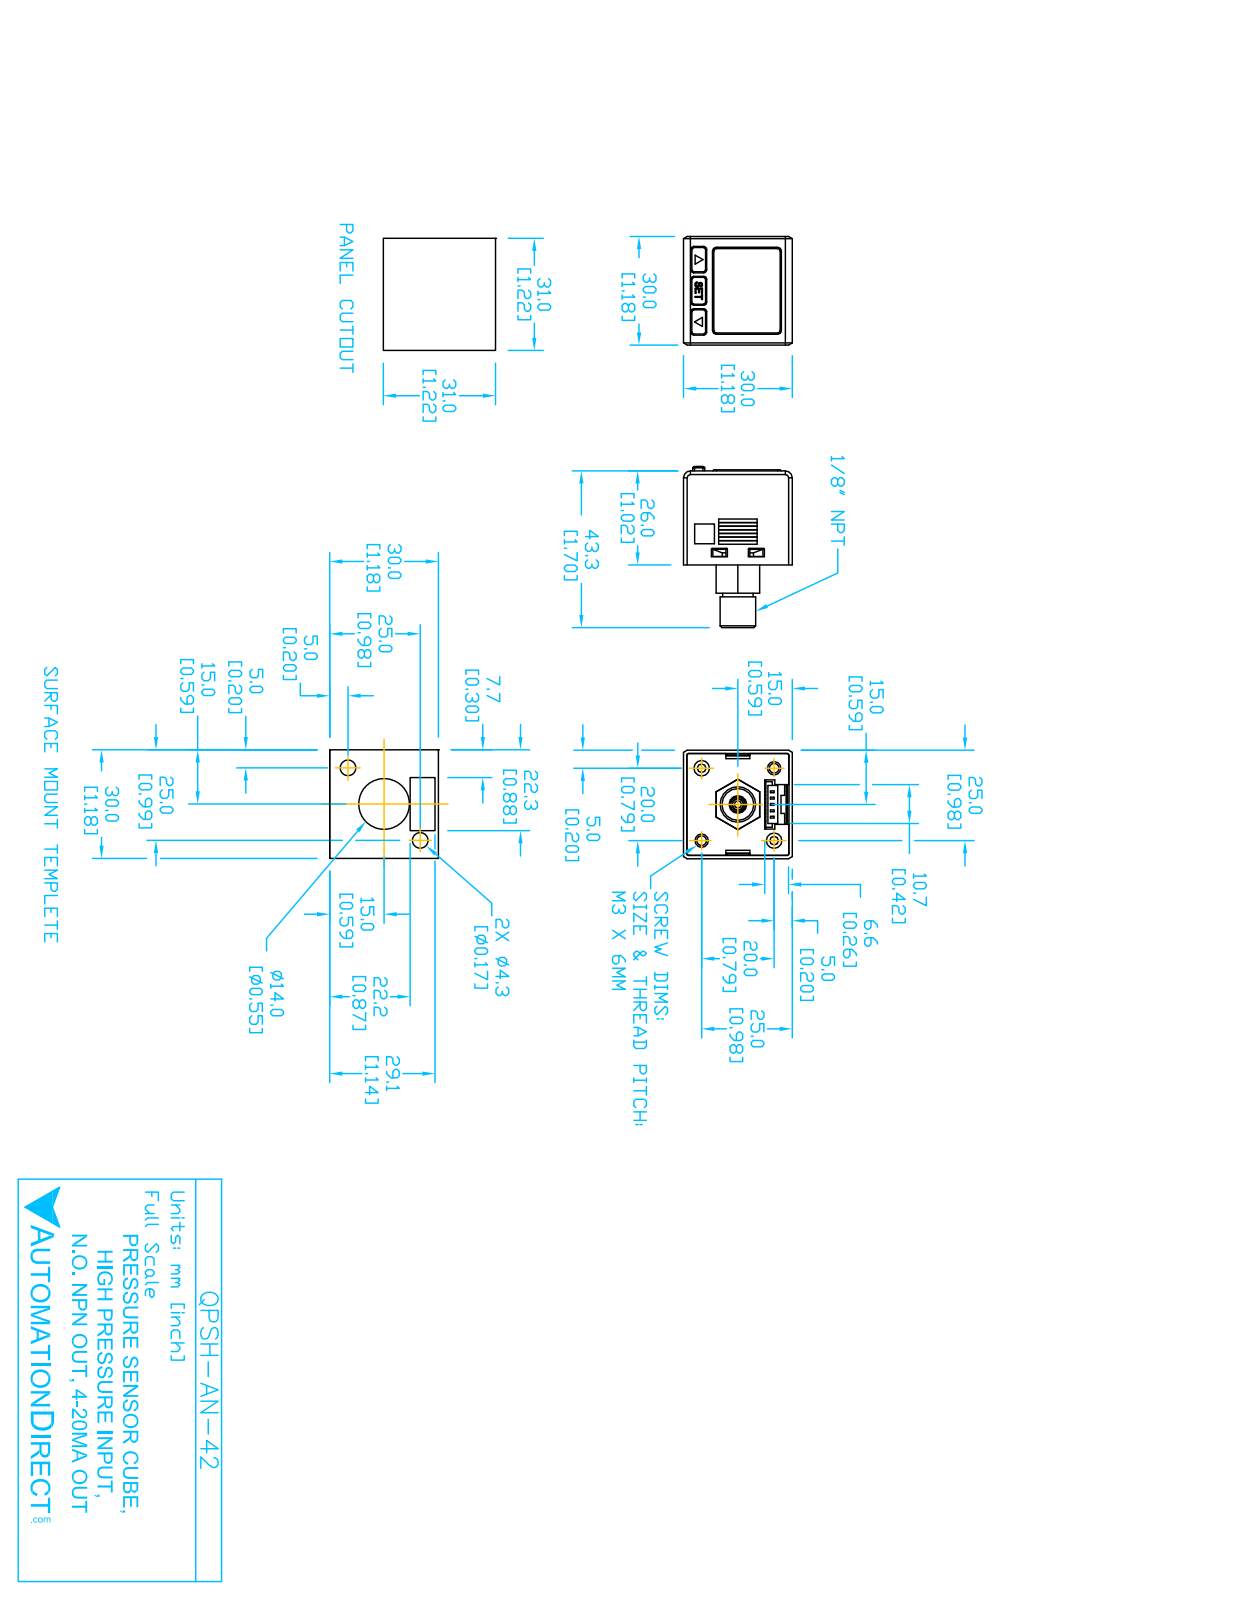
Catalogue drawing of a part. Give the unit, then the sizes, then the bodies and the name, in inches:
Units: inches
Overall size (bounding box): 1.806 × 1.18 × 1.18
Round holes (diameter × count): ⌀0.105 ×2, ⌀0.12 ×2, ⌀0.19 ×2, ⌀0.165 ×1
Round bosses / shafts (diameter × count): ⌀0.375 ×1, ⌀0.32 ×1
Partial cylindrical surfaces — rounded edges, fillets, slot ends (radius × count): R0.02 ×16, R0.015 ×8, R0.06 ×2
Main face-to-face distances: 1.18, 1.041, 1.04, 0.03, 0.04, 0.476, 0.052, 0.564, 0.061, 0.352
Hole centre spacings: 0.552, 0.78, 1.104
Volume: 1.496 in³ · Surface area: 10.41 in²
Bodies: 1 solid, 386 faces (296 planar, 62 cylindrical, 28 other)
Part name (STEP PRODUCT): QPSH-AN-42
STEP written by: SolidWorks 2014 (AUTOMOTIVE_DESIGN)
